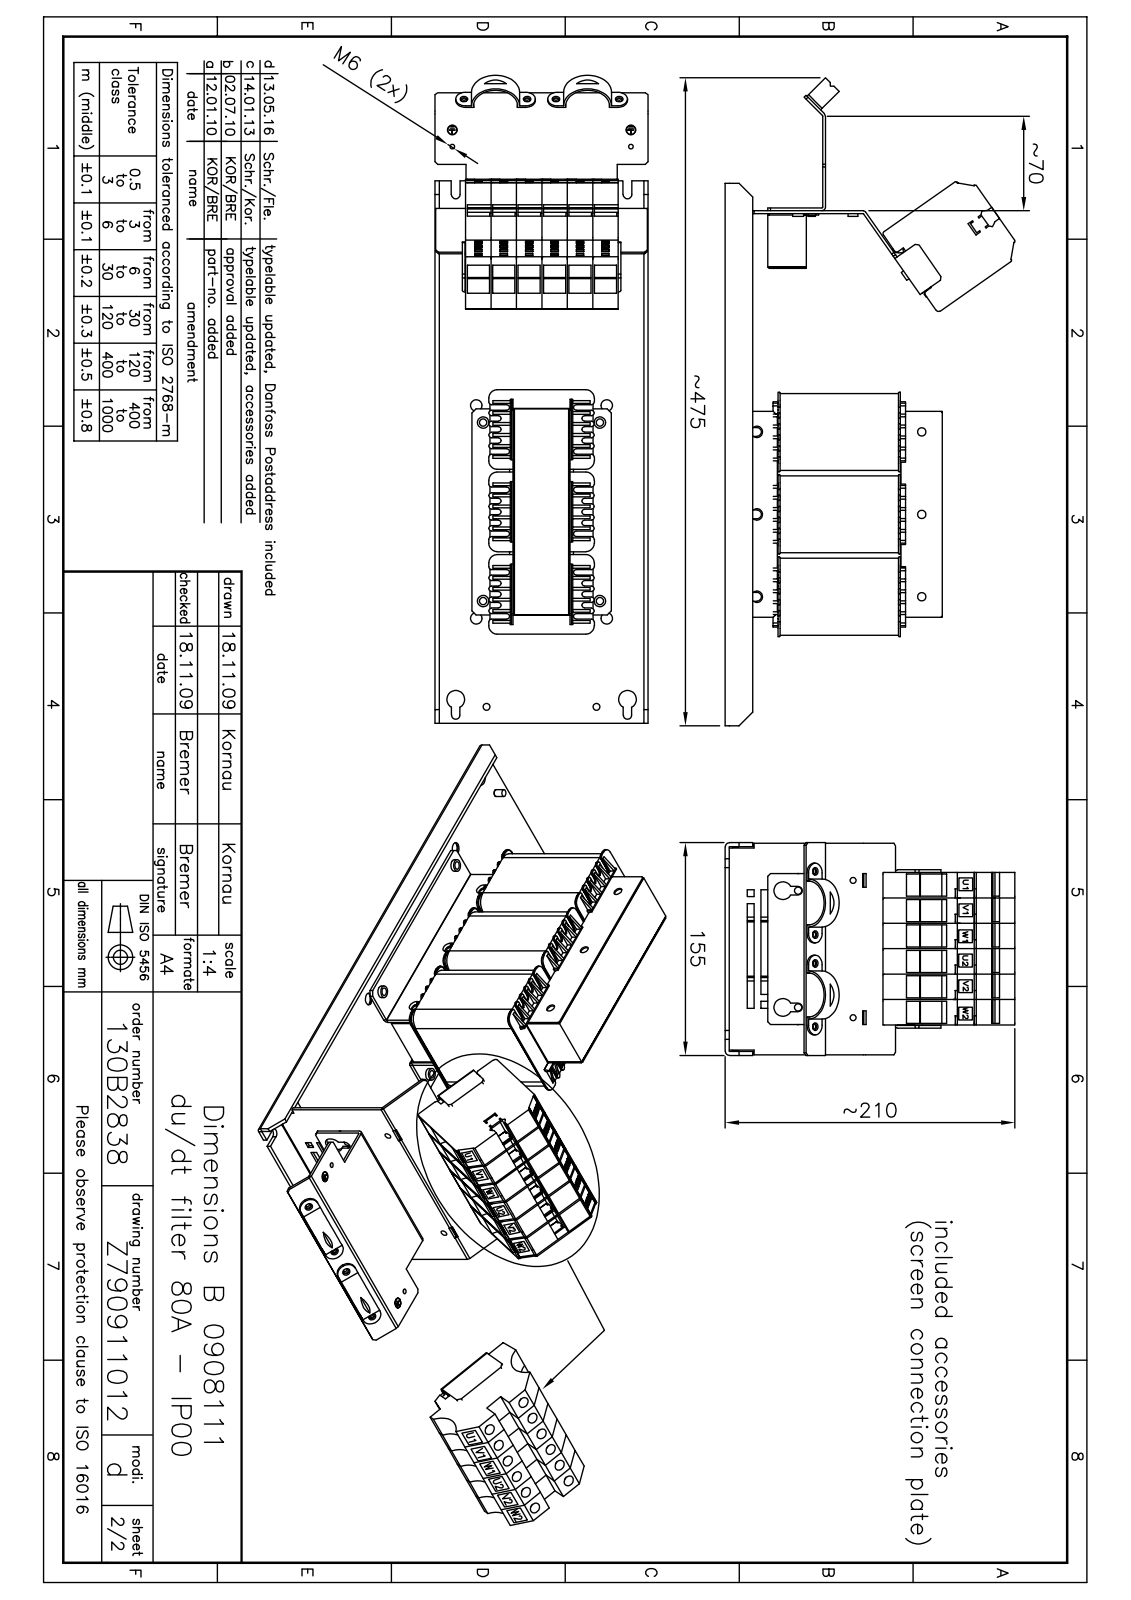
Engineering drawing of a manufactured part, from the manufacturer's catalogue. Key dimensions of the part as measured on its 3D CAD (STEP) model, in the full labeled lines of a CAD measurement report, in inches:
Part name (STEP PRODUCT): Wickel 3UI 90_41,5; WDU 50N beige +2210-0081; +1095-0157; hex nut gradec_din_Hexagon Nut ISO 4034 - M6 - N (+8 more)
STEP written by: SolidWorks 2014 (AUTOMOTIVE_DESIGN)
Units: inches
Bodies: 88 solids, 4386 faces (2926 planar, 852 cylindrical, 608 other)
Overall size (bounding box): 18.577 × 8.361 × 6.102
Volume: 141.4 in³ · Surface area: 1 334 in²
Round holes (diameter × count): ⌀0.236 ×15, ⌀0.335 ×13, ⌀0.197 ×12, ⌀0.217 ×10, ⌀0.252 ×10, ⌀0.311 ×6, ⌀0.146 ×4, ⌀0.24 ×4, ⌀0.281 ×4, ⌀0.512 ×4, ⌀0.315 ×3, ⌀0.201 ×2
Round bosses / shafts (diameter × count): ⌀0.472 ×10, ⌀0.315 ×8, ⌀0.709 ×6, ⌀0.445 ×6, ⌀0.465 ×4, ⌀0.394 ×4, ⌀0.276 ×4, ⌀0.274 ×4
Partial cylindrical surfaces — rounded edges, fillets, slot ends (radius × count): R0.02 ×76, R0.079 ×69, R0.008 ×28, R0.004 ×16, R0.394 ×14, R0.236 ×12, R0.039 ×9, R0.043 ×8
Main face-to-face distances: 0.118, 1.594, 0.039, 0.098, 2.362, 0.079, 1.457, 0.728, 0.472, 1.693
Hole centre spacings: 3.15, 0.53, 1.719, 2.362, 3.346, 3.577, 3.74, 4.724
